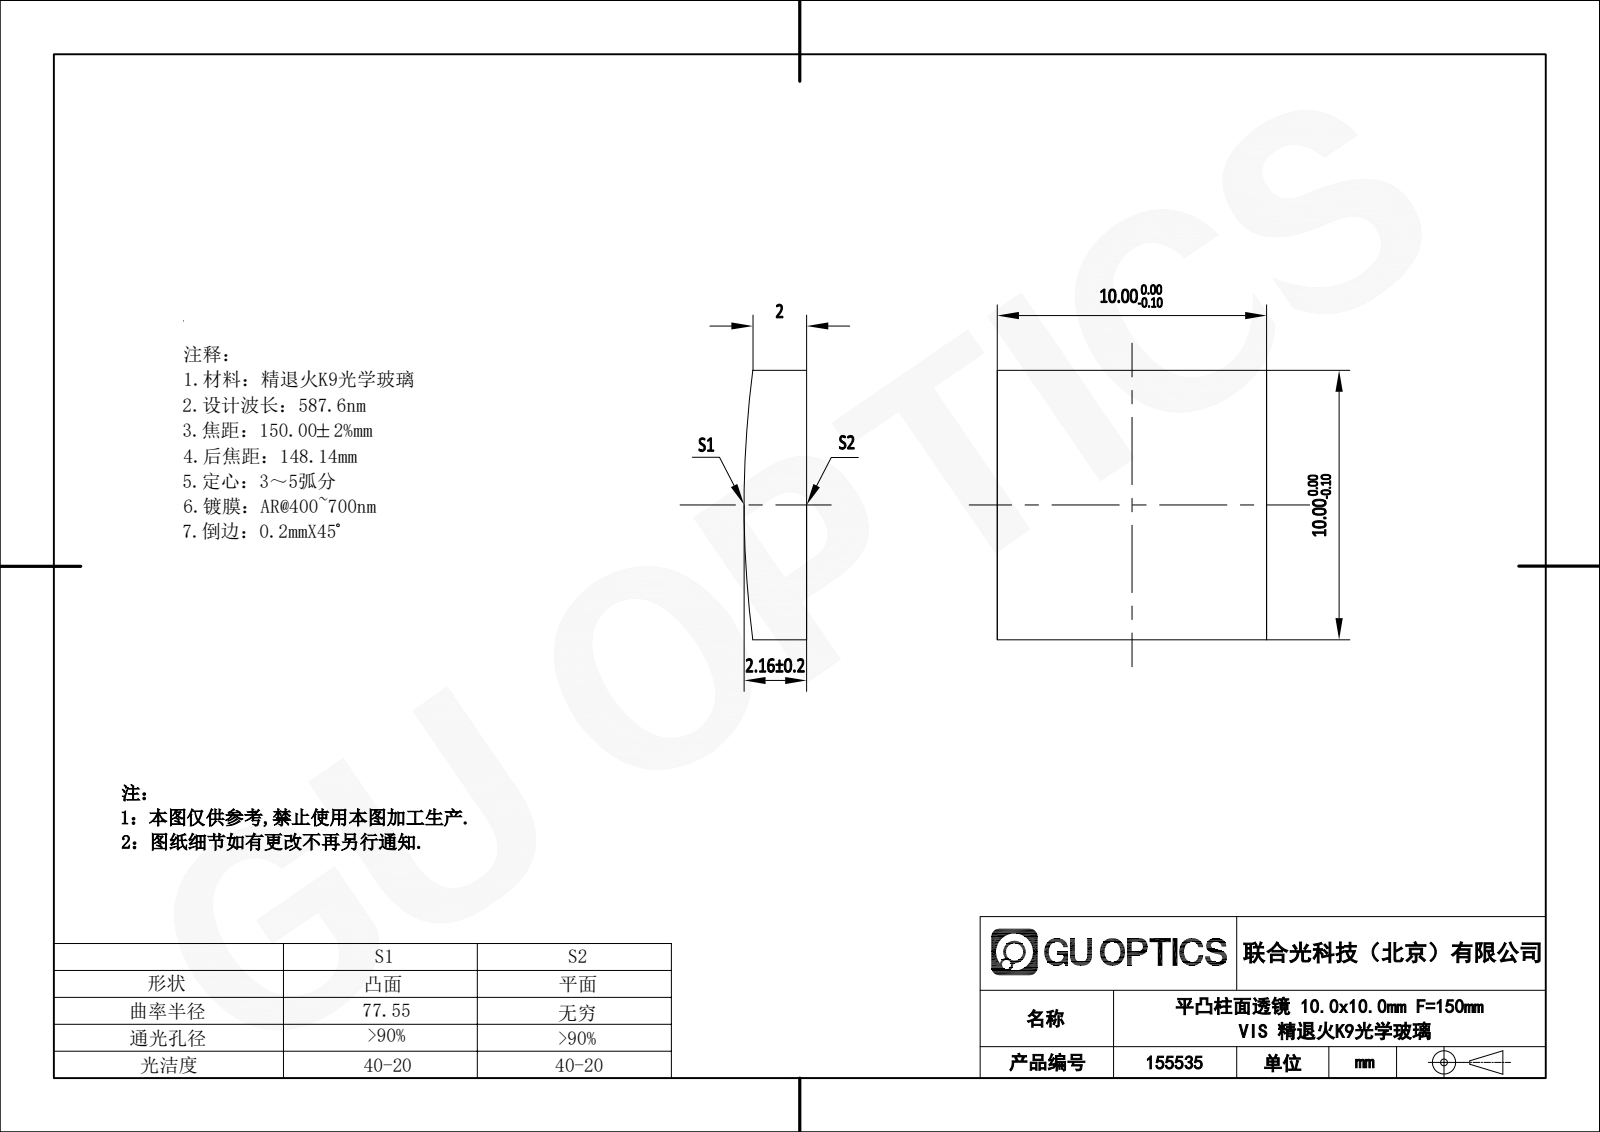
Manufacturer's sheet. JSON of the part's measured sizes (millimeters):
{"part_name": "155523", "step_written_by": "SolidWorks 2020 (CONFIG_CONTROL_DESIGN)", "units": "millimeters", "bodies": {"solids": 1, "faces": 7, "planar": 5, "cylindrical": 2, "other": 0}, "overall_size": [10, 10, 2.16], "volume_mm3": 211, "surface_area_mm2": 282, "partial_cylinders_radius": [[77.55, 1]], "face_to_face_distances": [10]}
